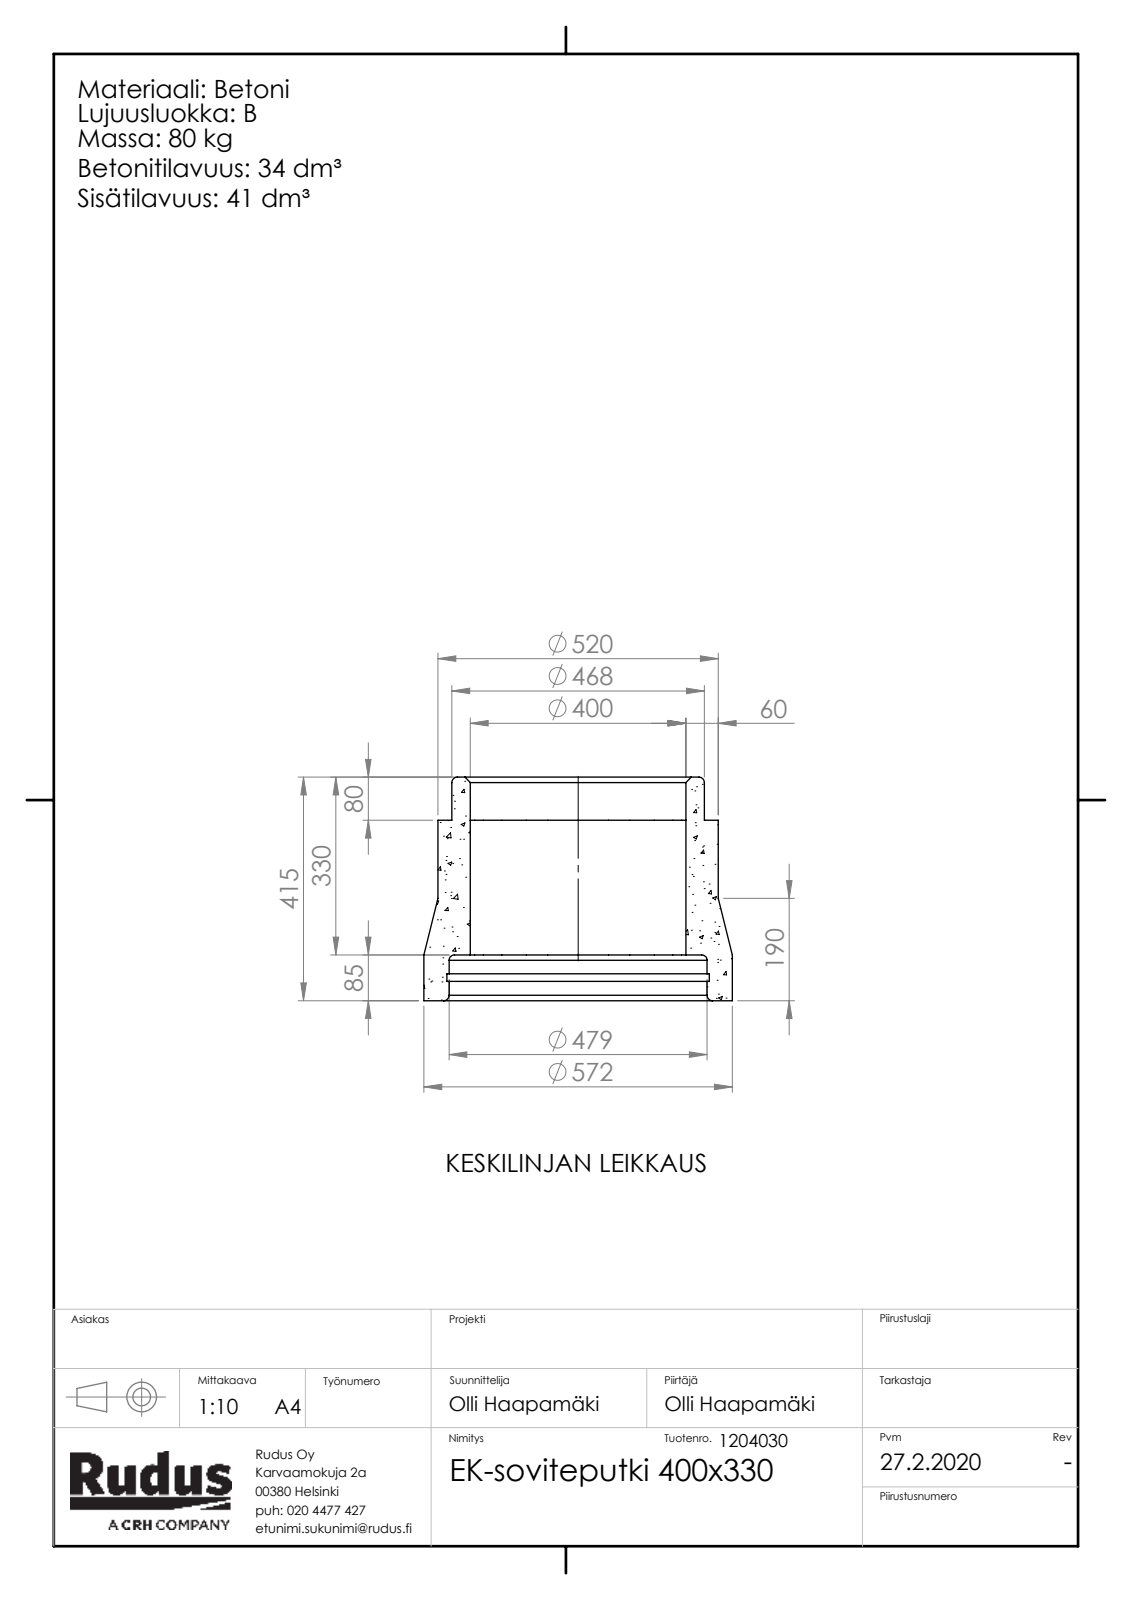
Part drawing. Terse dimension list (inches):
name: EK-osa-putkirunko; Rudus 1204030 EK-soviteputki 400x330
written by: SolidWorks 2019 (CONFIG_CONTROL_DESIGN)
unit: in
bodies: 1 solid, 66 faces (6 planar, 12 cylindrical, 48 other)
size: 22.52 × 22.52 × 16.339
volume: 2 079 in³; area: 2 234 in²
holes: 1× ⌀15.748, 1× ⌀18.843, 1× ⌀19.157
bosses: 1× ⌀22.52, 1× ⌀18.441
face distances: 13.189, 3.346, 9.843, 16.339, 12.992, 3.15, 1.969, 1.378, 11.22, 14.37
